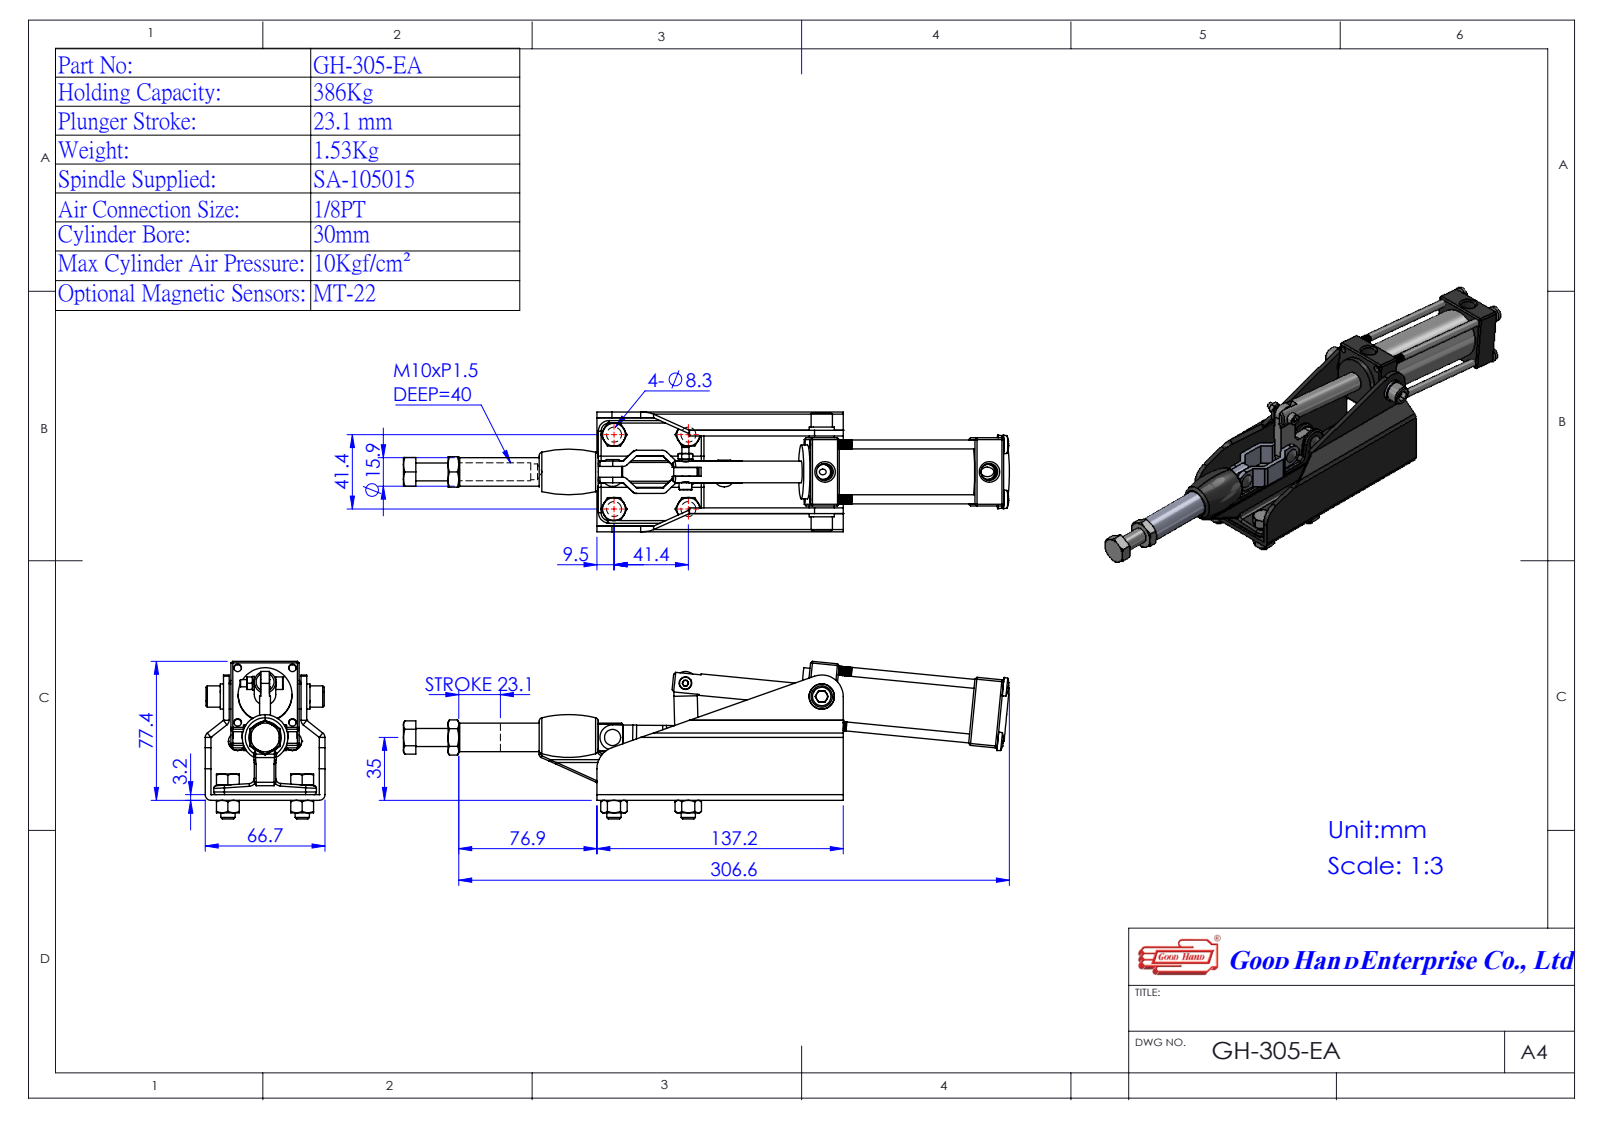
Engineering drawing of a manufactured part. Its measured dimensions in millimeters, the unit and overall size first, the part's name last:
Units: millimetres
Overall size (bounding box): 336.81 × 90.1 × 66.7
Round holes (diameter × count): ⌀5.5 ×3, ⌀7.9 ×2, ⌀4 ×1, ⌀6 ×1, ⌀8.5 ×1, ⌀12 ×1, ⌀30 ×1
Round bosses / shafts (diameter × count): ⌀8 ×5, ⌀5 ×5, ⌀13 ×4, ⌀10.3 ×4, ⌀30 ×3, ⌀6.3 ×2, ⌀32 ×1, ⌀15.88 ×1
Partial cylindrical surfaces — rounded edges, fillets, slot ends (radius × count): R1.5 ×17, R3 ×9, R3.21 ×6, R6.5 ×3, R7 ×2, R2 ×1, R4 ×1, R12 ×1
Main face-to-face distances: 3.2, 63.5, 10.15, 53.35, 60.3, 66.7, 36.65, 39.85, 26.85, 23.65
Hole centre spacings: 20, 20.75, 28.82, 41.2, 45.61, 58.89, 61.95, 75.25
Volume: 246 491 mm³ · Surface area: 114 769 mm²
Bodies: 7 solids, 799 faces (403 planar, 163 cylindrical, 233 other)
Part name (STEP PRODUCT): GH-305-EA(簡化); 1305EA02-1^GH-305-EA(簡化); 4305EA33-1^GH-305-EA(簡化); Group2^GH-305-EA(簡化) (+4 more)
STEP written by: SolidWorks 2016 (AUTOMOTIVE_DESIGN)
